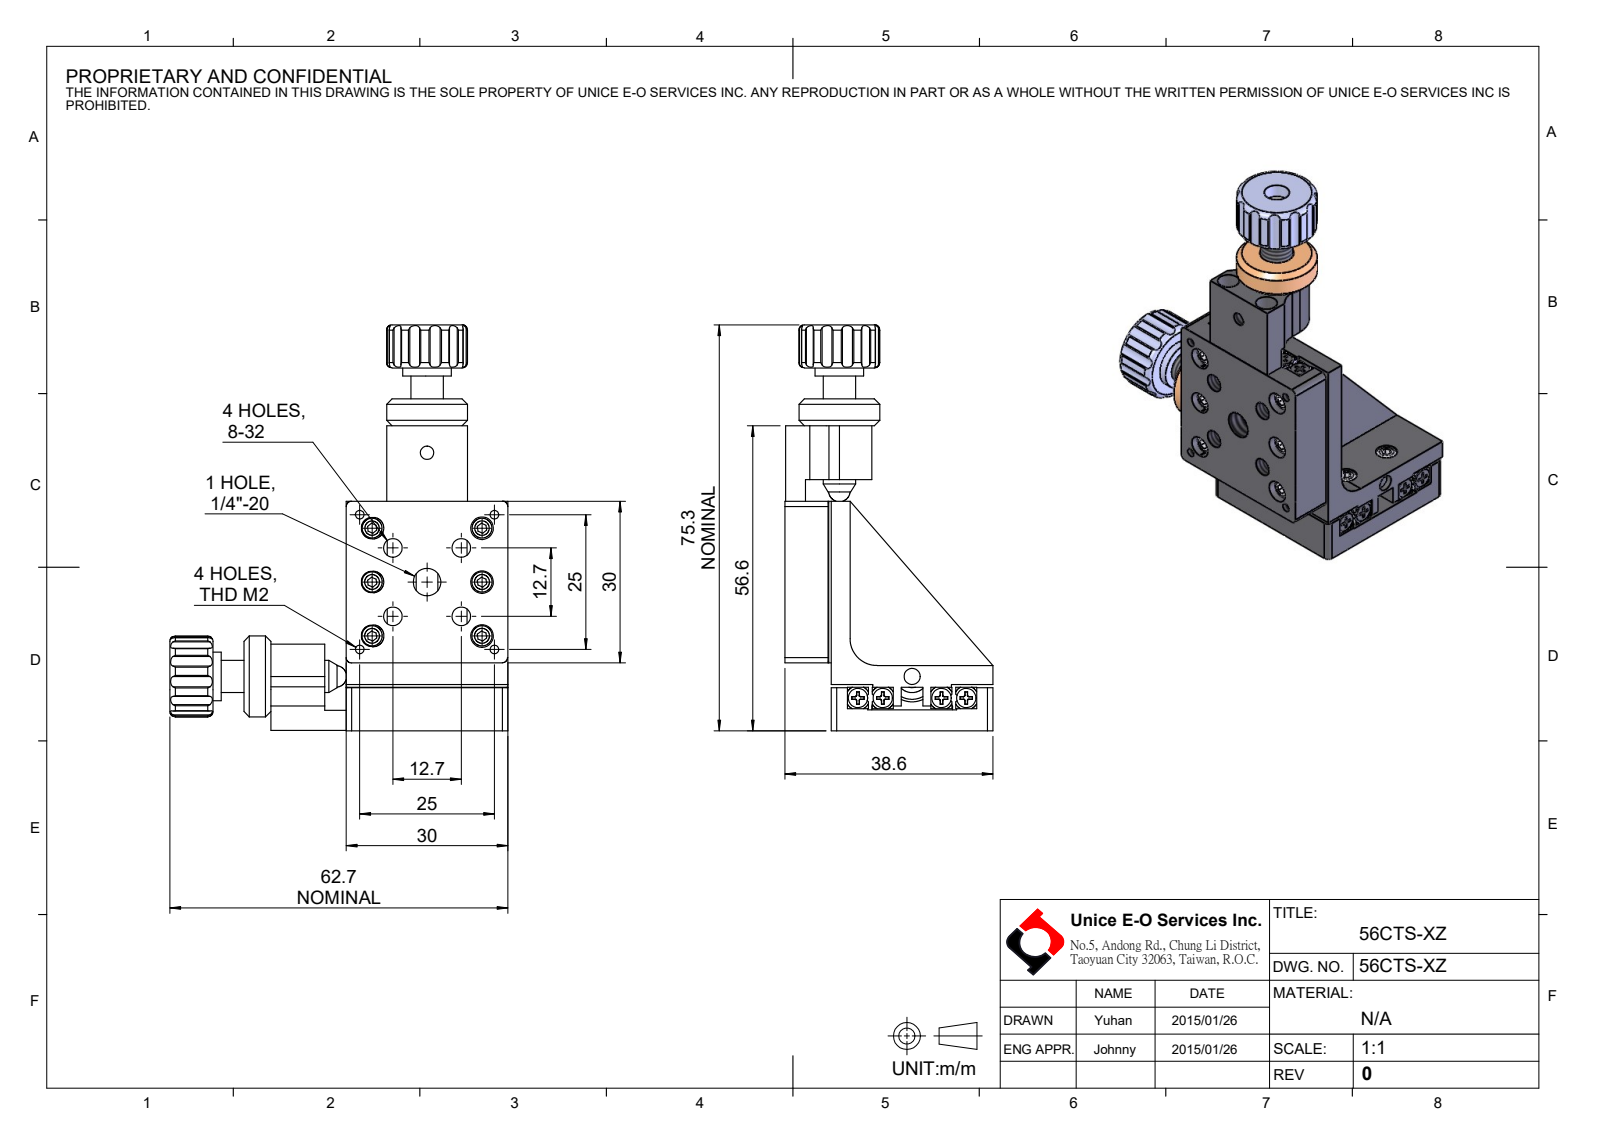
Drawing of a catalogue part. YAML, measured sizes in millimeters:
part_name: "56CTS-XZ"
step_written_by: "SolidWorks 2016 (CONFIG_CONTROL_DESIGN)"
units: millimeters
bodies: {solids: 73, faces: 1850, planar: 874, cylindrical: 626, other: 350}
overall_size: [75.33, 62.73, 38.6]
volume: 29350
surface_area: 29864
round_holes:
  - {diameter: 1.6, count: 48}
  - {diameter: 4, count: 18}
  - {diameter: 2.2, count: 12}
  - {diameter: 2.5, count: 8}
  - {diameter: 3.45, count: 8}
  - {diameter: 2.6, count: 6}
  - {diameter: 4.2, count: 6}
  - {diameter: 2.1, count: 4}
  - {diameter: 3, count: 2}
  - {diameter: 4.7, count: 2}
  - {diameter: 5.11, count: 2}
  - {diameter: 5.9, count: 2}
round_bosses_or_shafts:
  - {diameter: 3.7, count: 25}
  - {diameter: 2, count: 25}
  - {diameter: 3.6, count: 8}
  - {diameter: 1.95, count: 8}
  - {diameter: 3, count: 6}
  - {diameter: 15, count: 2}
  - {diameter: 9, count: 2}
partial_cylinders:
  - {radius: 0.3, count: 48}
  - {radius: 1.5, count: 24}
  - {radius: 1.25, count: 12}
  - {radius: 2, count: 12}
  - {radius: 1, count: 8}
  - {radius: 5, count: 5}
  - {radius: 6, count: 2}
face_to_face_distances: [4, 8, 0.5, 4.1, 3.9, 8.1, 4.5, 3.5, 8.5, 12]
hole_center_spacings: [15.5, 10, 19.83, 11.14, 18.45, 4.9, 12.54, 17.73]
